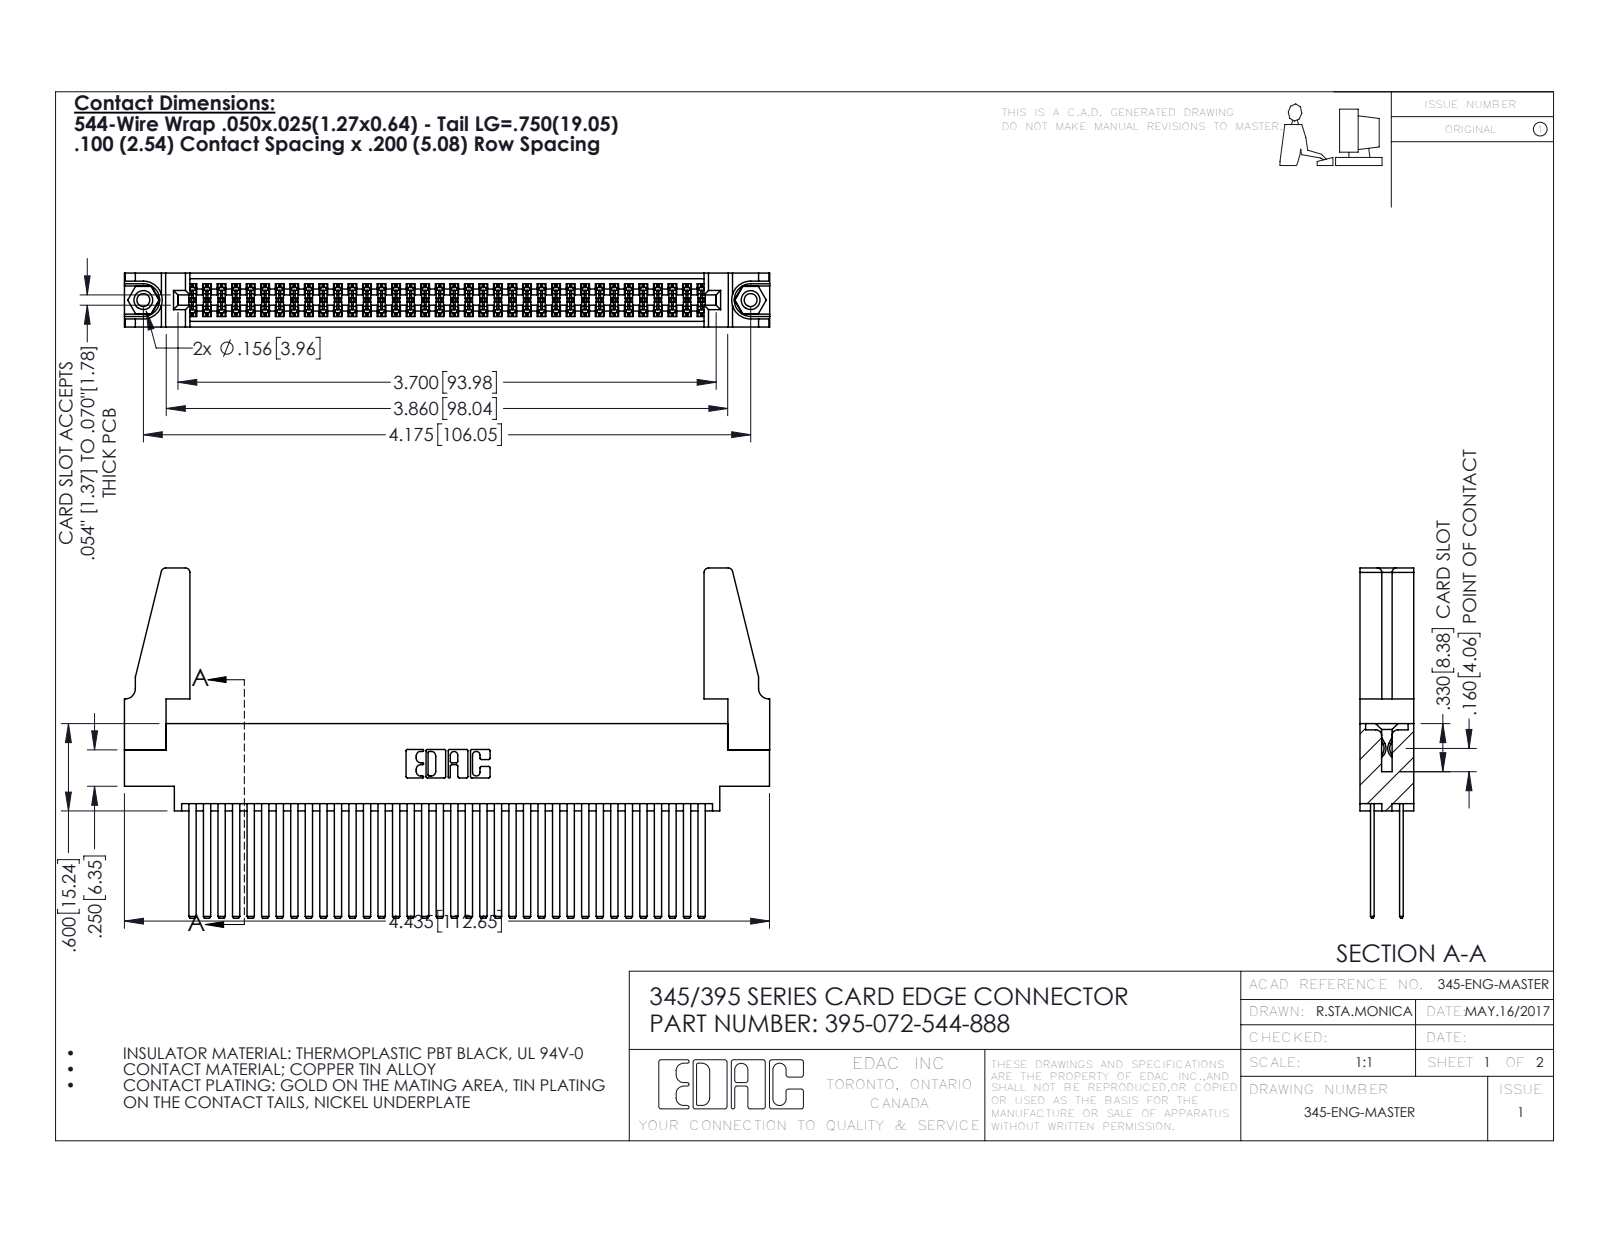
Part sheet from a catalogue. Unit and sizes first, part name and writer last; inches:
Units: inches
Overall size (bounding box): 4.436 × 2.407 × 0.37
Round holes (diameter × count): ⌀0.089 ×2, ⌀0.125 ×2, ⌀0.156 ×2, ⌀0.064 ×1
Round bosses / shafts (diameter × count): ⌀0.155 ×2
Partial cylindrical surfaces — rounded edges, fillets, slot ends (radius × count): R0.006 ×108, R0.01 ×22, R0.03 ×8, R0.007 ×6, R0.031 ×6, R0.026 ×3, R0.014 ×2, R0.019 ×2
Main face-to-face distances: 0.072, 0.298, 0.2, 0.098, 0.272, 0.025, 0.37, 0.225, 0.175, 0.149
Hole centre spacings: 0.27, 3.939, 4.175
Volume: 0.918 in³ · Surface area: 36.47 in²
Bodies: 77 solids, 3422 faces (2244 planar, 1162 cylindrical, 16 other)
Part name (STEP PRODUCT): 345-250-001_345-250-001-102; 345 Part_0.170 Offset - 0.156 Dia-TH; 345-220-078_345-220-088; 395-072-544-888 (+1 more)
STEP written by: SolidWorks 2016 (CONFIG_CONTROL_DESIGN)
